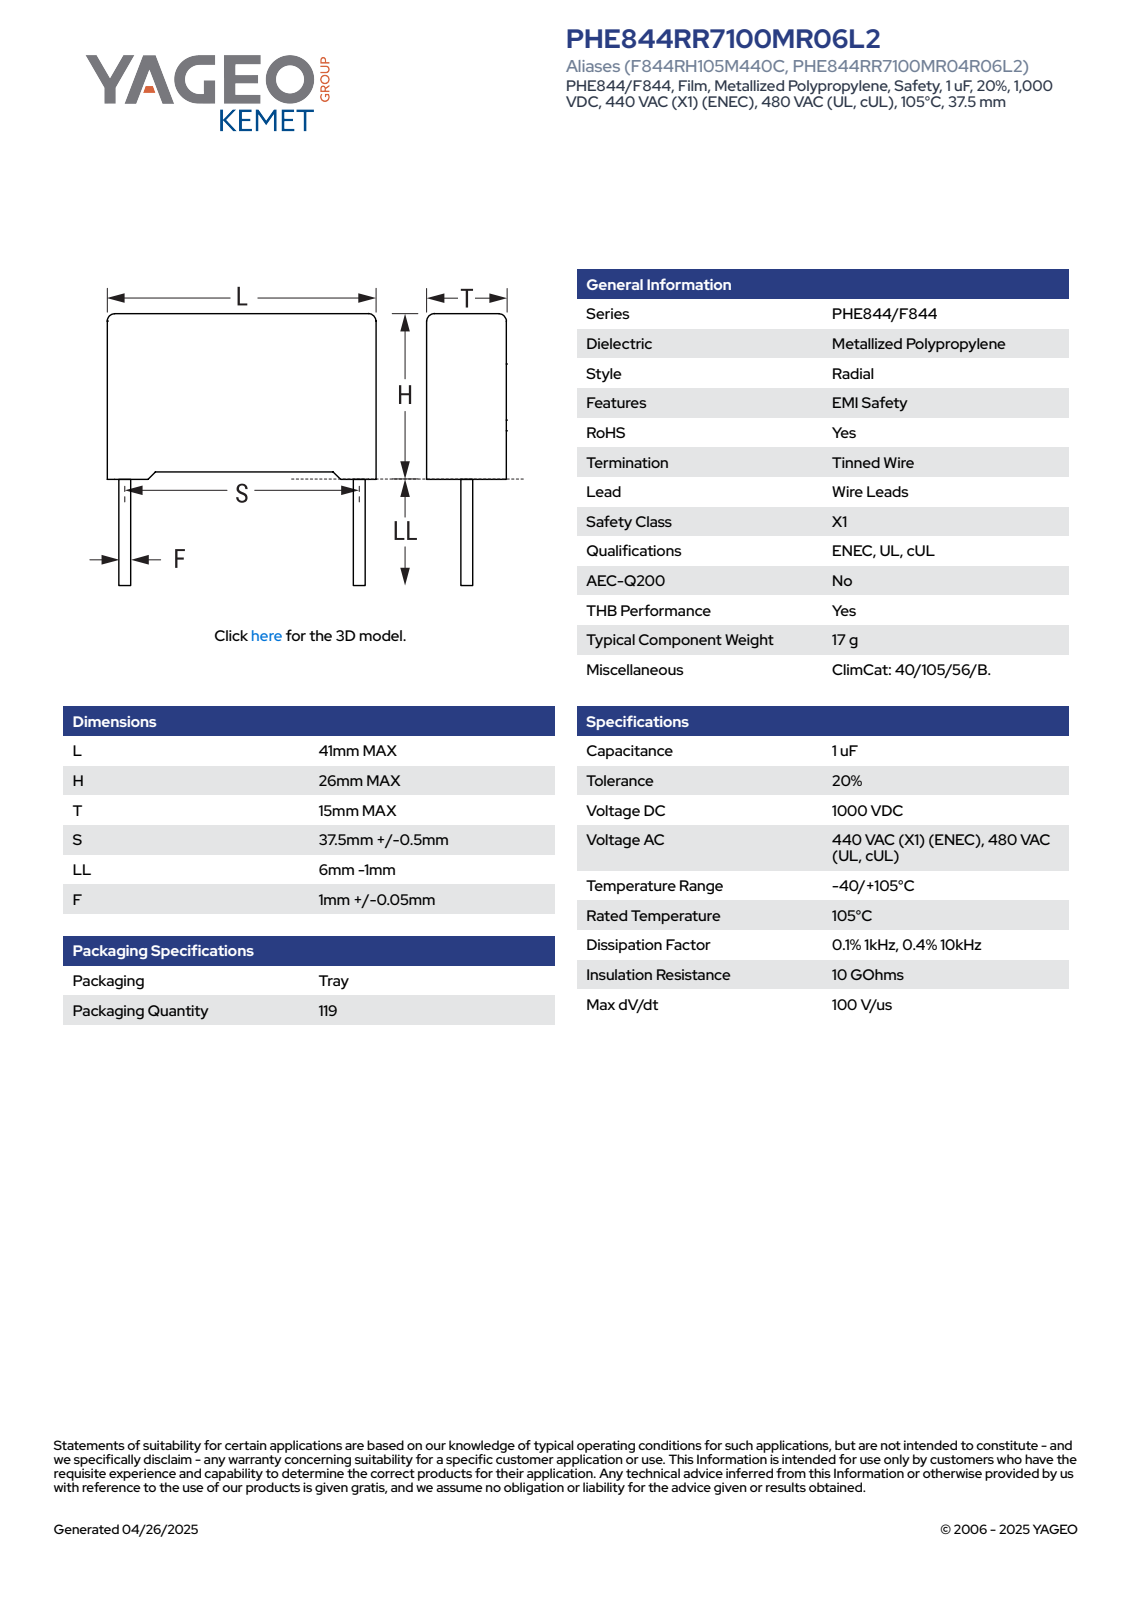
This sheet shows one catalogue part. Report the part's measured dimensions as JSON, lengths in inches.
{"part_name": "CFR_RB2_41X26X15_L41H26T15S37.5LL5F1.05", "step_written_by": "SolidWorks 2021 (AUTOMOTIVE_DESIGN)", "units": "inches", "bodies": {"solids": 4, "faces": 87, "planar": 79, "cylindrical": 8, "other": 0}, "overall_size": [1.614, 1.22, 0.591], "volume_in3": 0.946, "surface_area_in2": 6.584, "round_bosses_or_shafts": [[0.041, 2]], "partial_cylinders_radius": [[0.02, 4]], "face_to_face_distances": [0.591, 0.988, 1.614, 0.994, 0.03, 0.035, 1.024, 0.054, 1.56, 1.506]}
